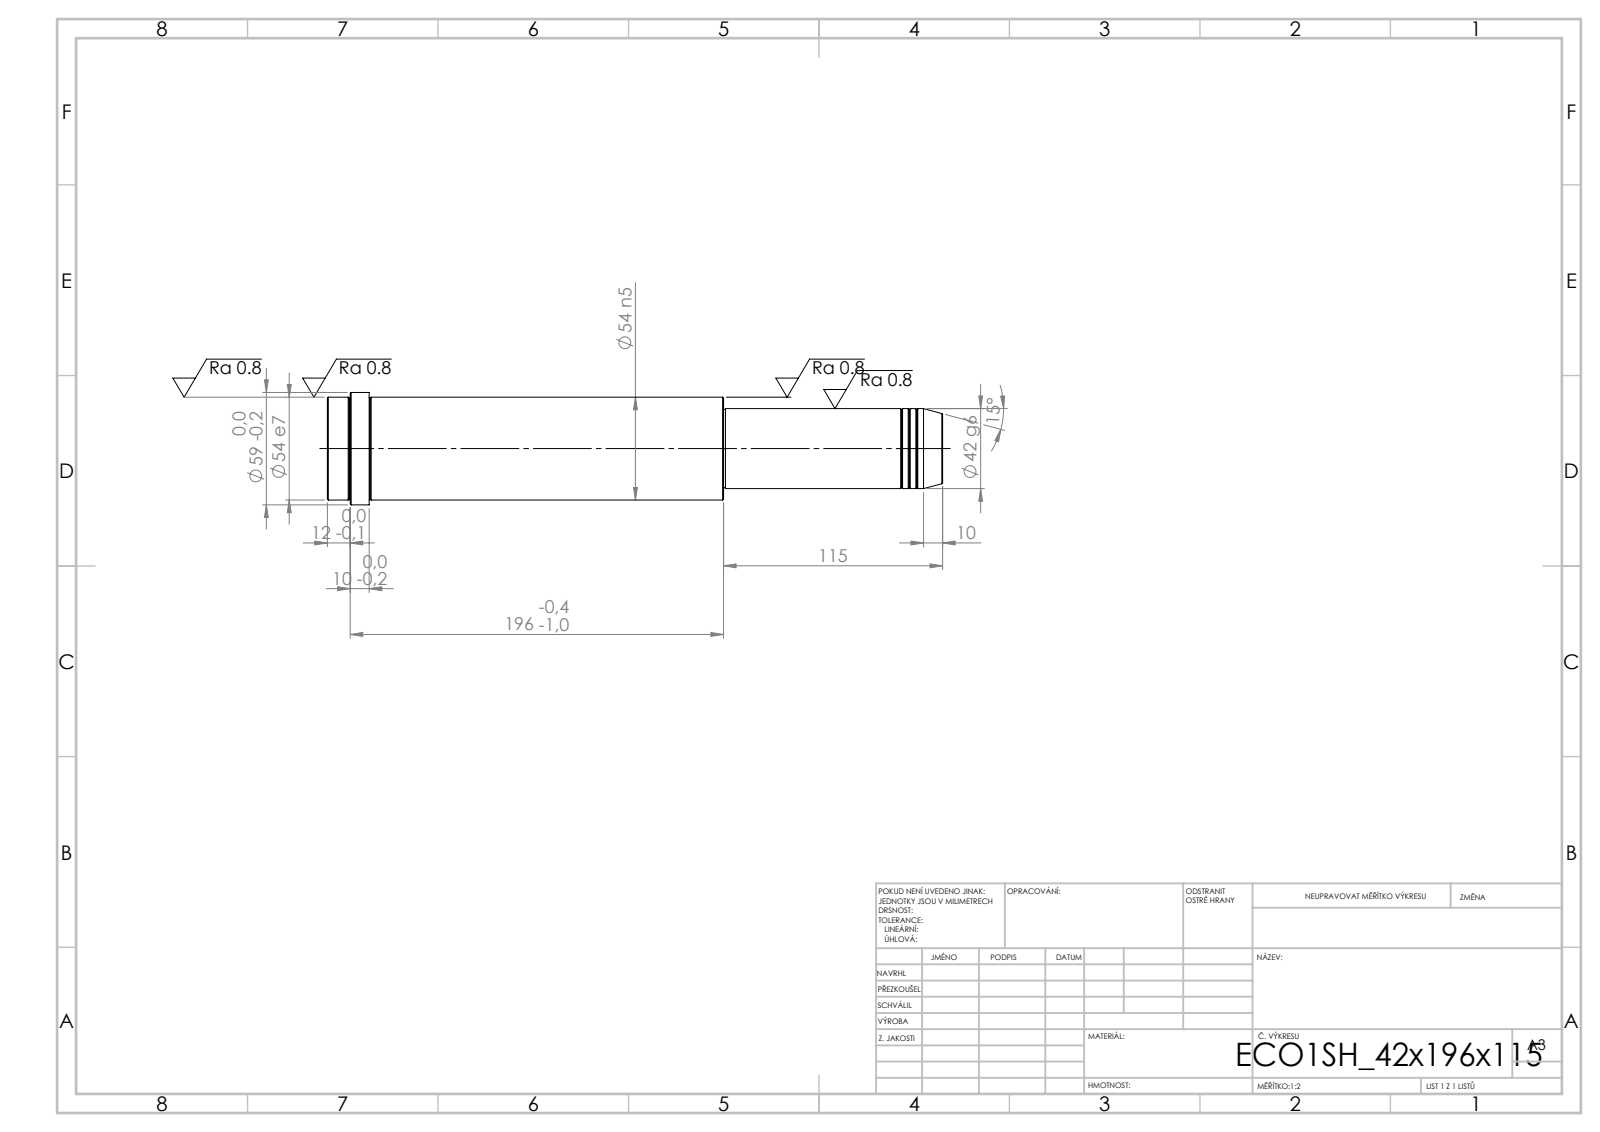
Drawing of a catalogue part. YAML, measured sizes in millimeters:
step_written_by: "SolidWorks 2019 (CONFIG_CONTROL_DESIGN)"
units: millimeters
bodies: {solids: 1, faces: 52, planar: 6, cylindrical: 16, other: 30}
overall_size: [323, 59, 59]
volume: 638017
surface_area: 56077
round_bosses_or_shafts:
  - {diameter: 59, count: 1}
  - {diameter: 54, count: 1}
  - {diameter: 42, count: 1}
  - {diameter: 41, count: 1}
face_to_face_distances: [323, 115, 208, 301, 186, 22, 311, 196, 10, 12]
